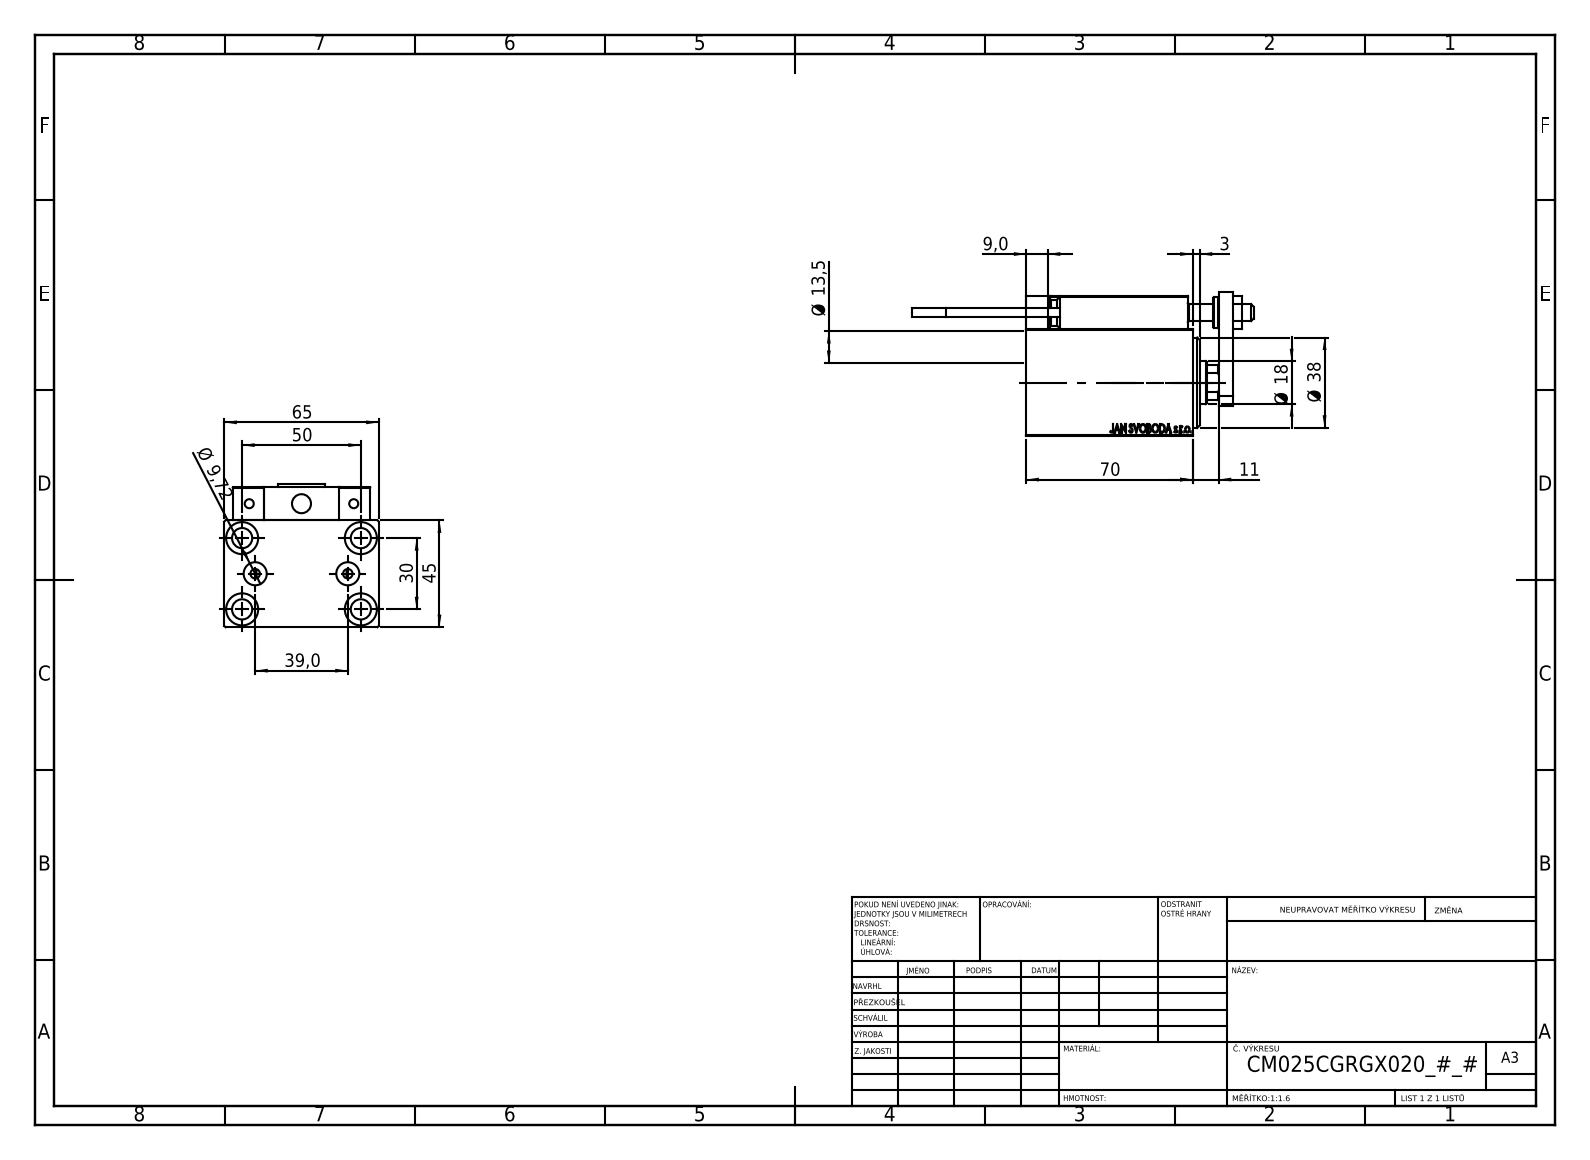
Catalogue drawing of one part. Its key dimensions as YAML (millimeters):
part_name: "ALLEN BOLT D5; TYC_L79; V450CM_C_VCP; MAGNET (+7 more)"
step_written_by: "SolidWorks 2019 (CONFIG_CONTROL_DESIGN)"
units: millimeters
bodies: {solids: 23, faces: 1278, planar: 560, cylindrical: 184, other: 534}
overall_size: [143.7, 65, 60.5]
volume: 223993
surface_area: 69960
round_holes:
  - {diameter: 4, count: 6}
  - {diameter: 8, count: 5}
  - {diameter: 8.5, count: 5}
  - {diameter: 3.2, count: 4}
  - {diameter: 13.5, count: 4}
  - {diameter: 5, count: 2}
  - {diameter: 9.72, count: 2}
  - {diameter: 7, count: 1}
  - {diameter: 14.5, count: 1}
  - {diameter: 18, count: 1}
  - {diameter: 21.5, count: 1}
  - {diameter: 25, count: 1}
round_bosses_or_shafts:
  - {diameter: 5, count: 2}
  - {diameter: 3.8, count: 2}
  - {diameter: 13, count: 1}
  - {diameter: 11, count: 1}
partial_cylinders:
  - {radius: 0.3, count: 30}
  - {radius: 3, count: 2}
  - {radius: 8.5, count: 1}
face_to_face_distances: [45, 65, 59, 14, 6, 3, 19, 5, 7, 20]
hole_center_spacings: [15.98, 29.15, 46.96, 11.37, 19.5, 20, 22.09, 28.9]
